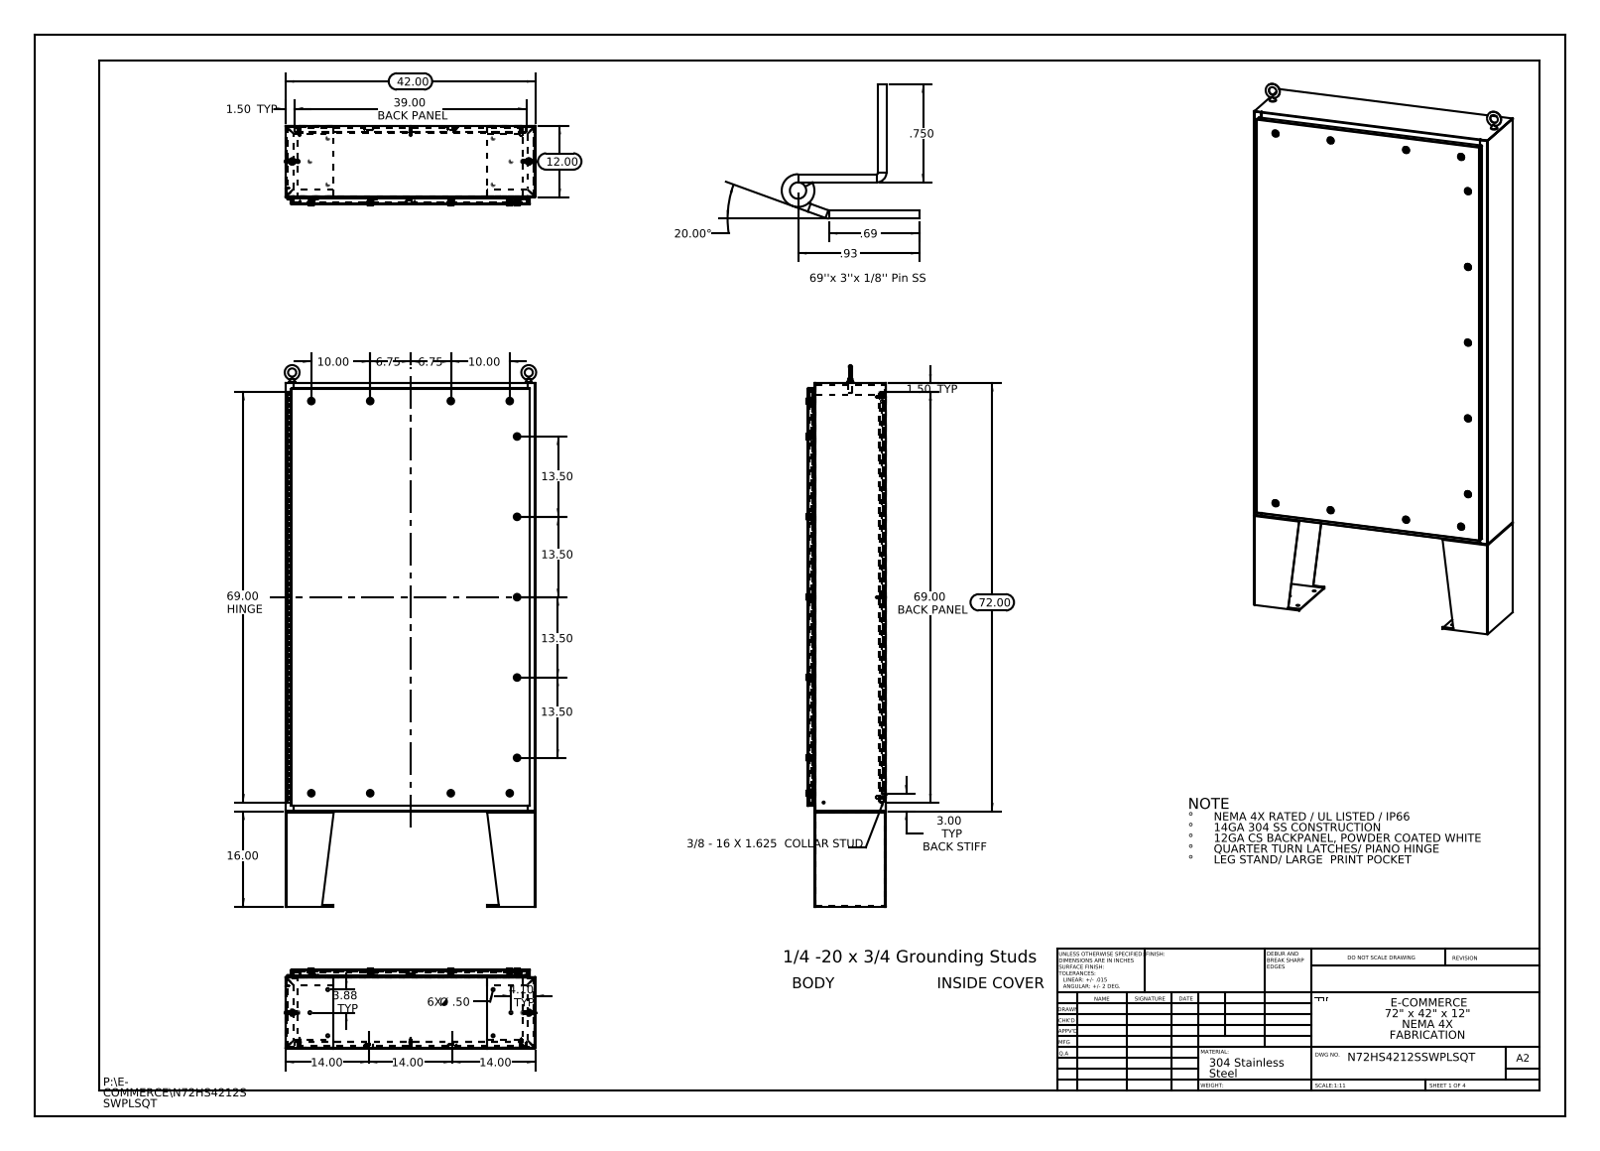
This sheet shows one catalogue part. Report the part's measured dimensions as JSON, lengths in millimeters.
{"part_name": "N72HS4212SSWPLSQT Cover; N72HS4212SSWPLSQT Mounting Studs; N72HS4212SSWPLSQT Body; N72HS4212SSWPLSQT Hinge Cover Side (+8 more)", "step_written_by": "SolidWorks 2013 (CONFIG_CONTROL_DESIGN)", "units": "millimeters", "bodies": {"solids": 36, "faces": 2647, "planar": 1331, "cylindrical": 1120, "other": 196}, "overall_size": [2311.4, 1073.7, 335.3], "volume_mm3": 19340000, "surface_area_mm2": 18400000, "round_holes": [[12.7, 14], [6.4, 8], [19.1, 4], [3.2, 1], [3.2, 1]], "round_bosses_or_shafts": [[15.9, 10], [9.5, 8], [8.4, 8], [4, 8], [3.6, 8], [8, 2], [6, 2], [6.4, 1]], "partial_cylinders_radius": [[0.3, 36], [2.2, 30], [1, 8], [3.6, 8], [11.2, 8], [0.5, 6], [3, 4], [3.2, 4]], "face_to_face_distances": [1.9, 333.4, 2.6, 331.5, 27.3, 335.3, 308, 25.4, 306.1, 29.9], "hole_center_spacings": [56.5, 181.3, 788.3, 854.1, 863.7, 863.8, 976.4, 1274.6]}
